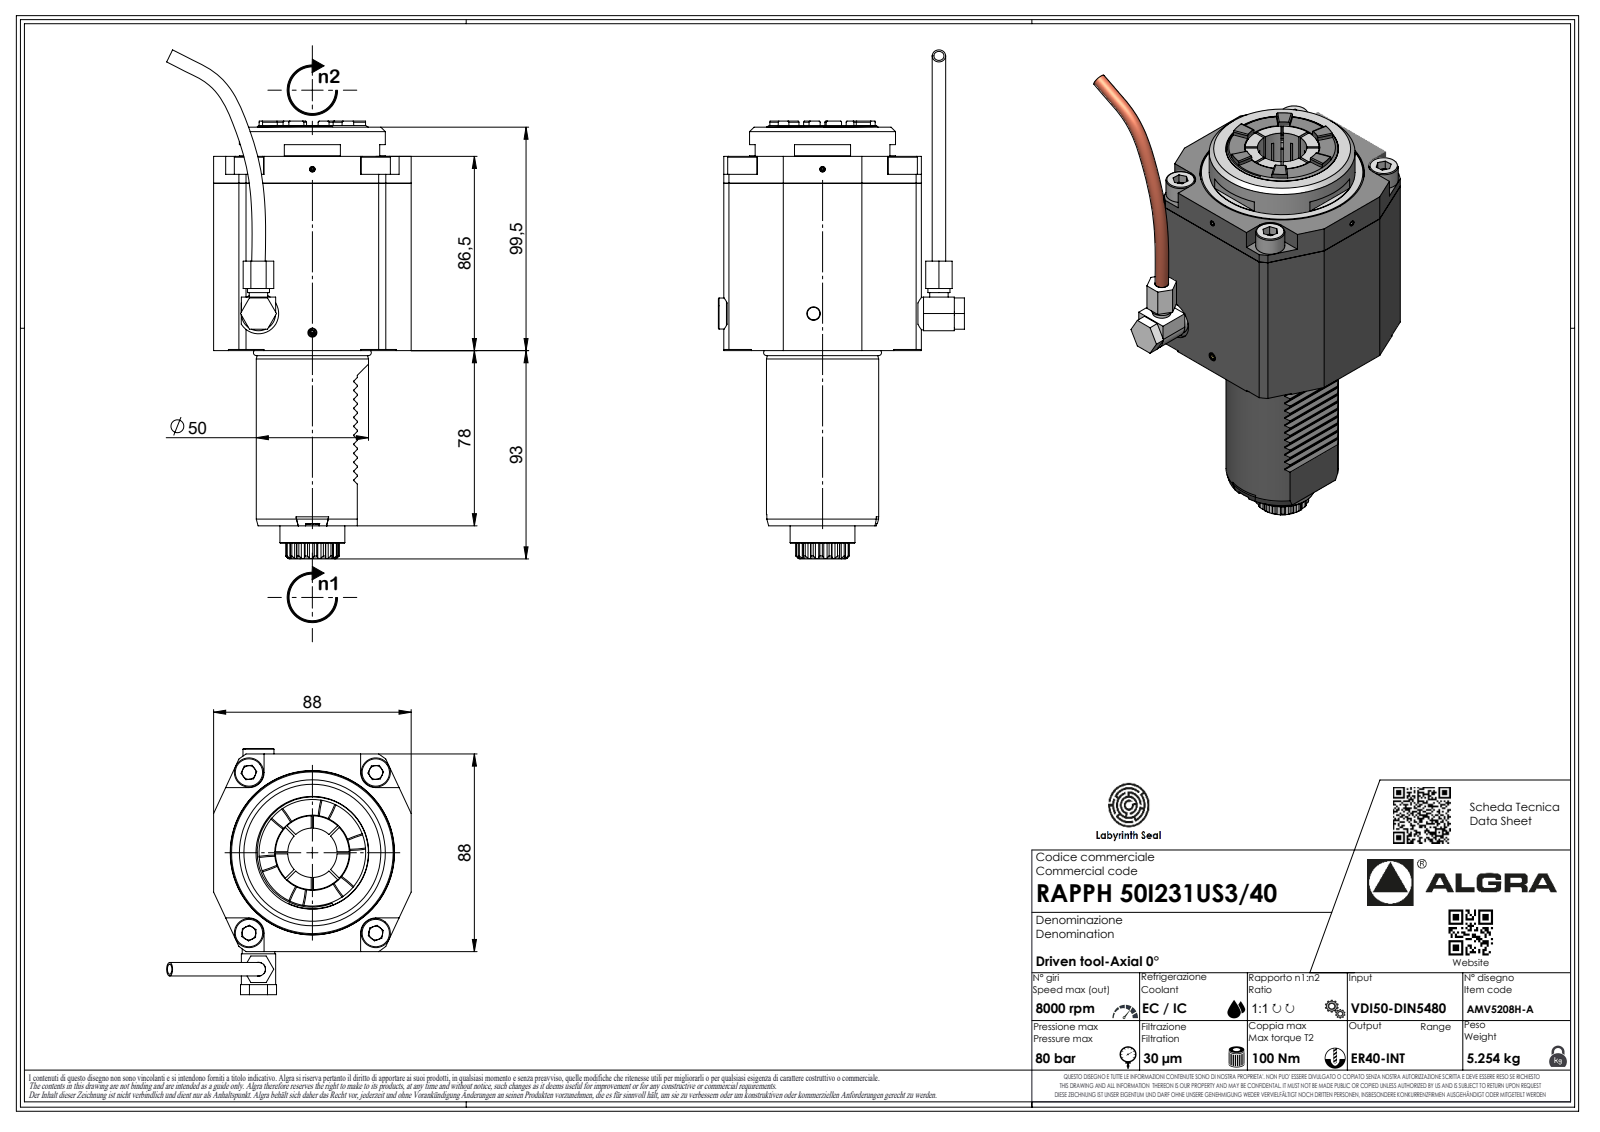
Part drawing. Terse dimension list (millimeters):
name: RAPPH50I231US340
written by: SolidWorks 2023 (AUTOMOTIVE_DESIGN)
unit: mm
bodies: 6 solids, 619 faces (345 planar, 120 cylindrical, 154 other)
size: 192.25 × 90.4 × 88
volume: 807 235 mm³; area: 59 175 mm²
holes: 1× ⌀2.1, 1× ⌀2.5, 1× ⌀31
bosses: 2× ⌀2.3, 1× ⌀65, 1× ⌀57.24, 1× ⌀50, 1× ⌀28.9, 1× ⌀13.8, 1× ⌀6.37, 1× ⌀5.7
rounds: 36× R1.61, 12× R0.3, 7× R0.33, 7× R0.52, 7× R3.7, 1× R0.21, 1× R3, 1× R11.88
face distances: 88, 96.2, 86.5, 99.5, 13, 2.83, 14.14, 78, 164.5, 177.5
hole spacings: 21
